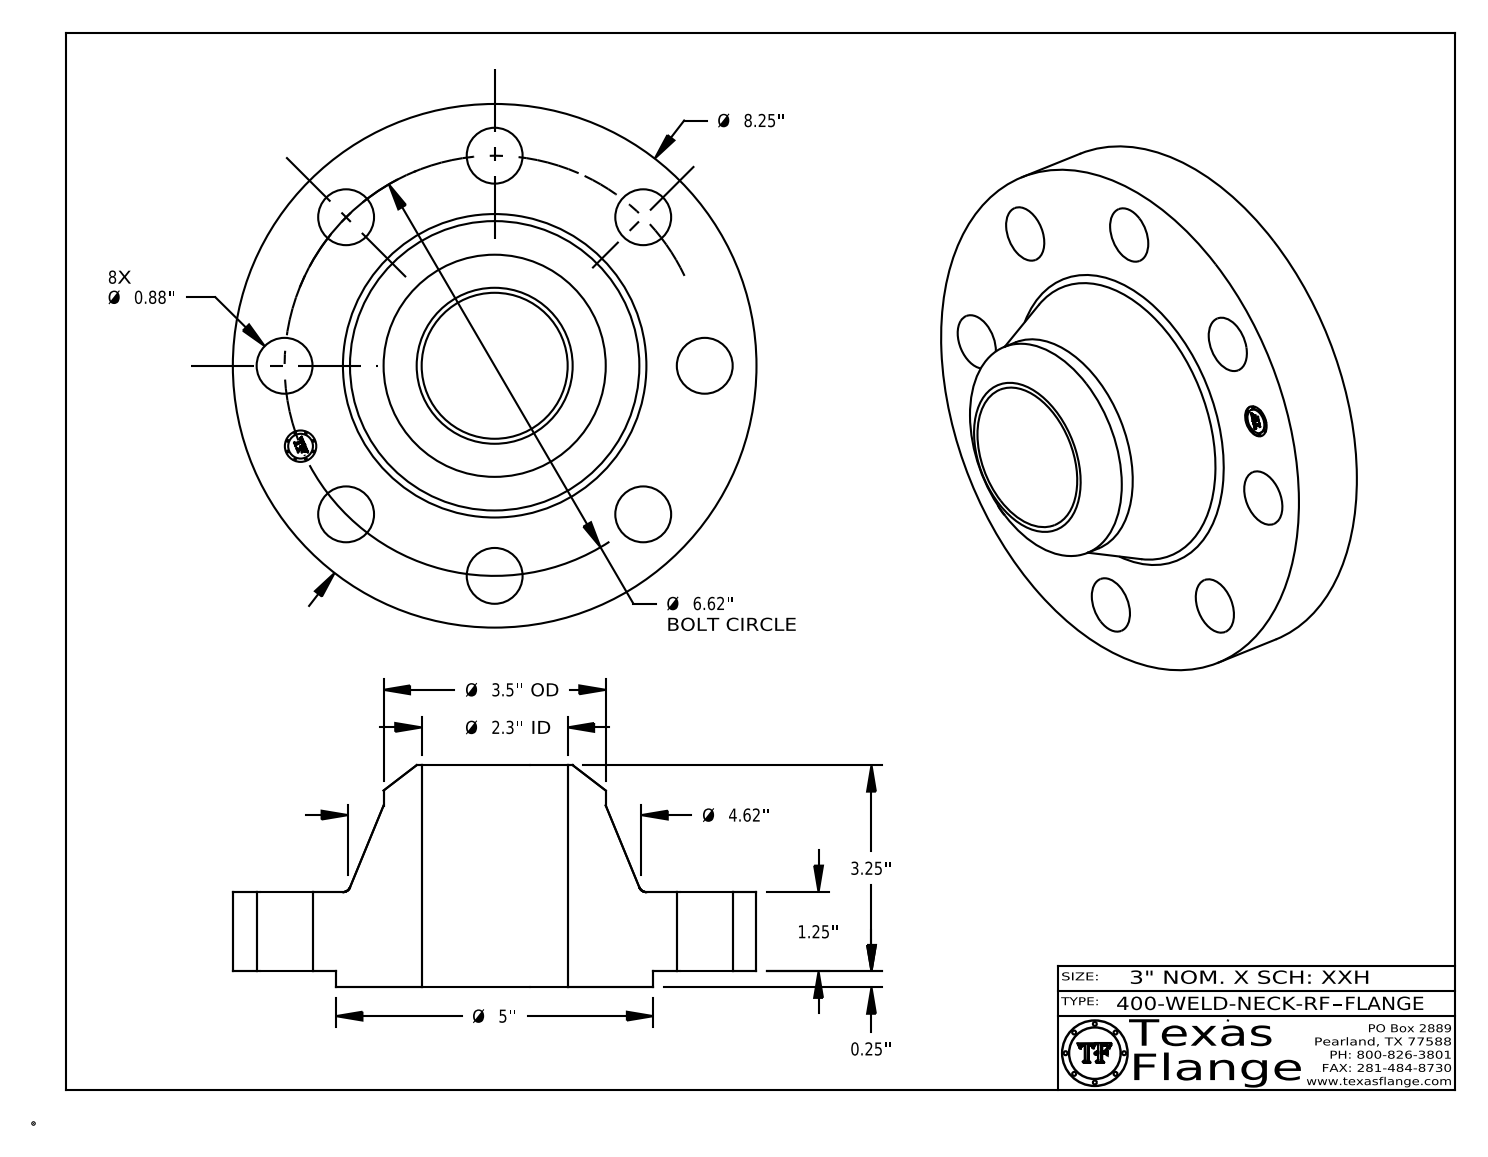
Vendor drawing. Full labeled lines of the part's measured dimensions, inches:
Part name (STEP PRODUCT): 400-WELD-NECK-RF
STEP written by: CATIA V5 STEP AP214 (AUTOMOTIVE_DESIGN)
Units: inches
Bodies: 1 solid, 419 faces (369 planar, 44 cylindrical, 6 other)
Overall size (bounding box): 8.25 × 8.25 × 3.5
Volume: 73.98 in³ · Surface area: 193.5 in²
Round holes (diameter × count): ⌀0.88 ×8, ⌀0.495 ×1, ⌀2.3 ×1
Round bosses / shafts (diameter × count): ⌀0.03 ×8, ⌀8.25 ×1, ⌀5 ×1, ⌀3.5 ×1, ⌀0.39 ×1
Main face-to-face distances: 1.25, 0.25, 1.5, 3.5, 3.25, 2, 0.015, 1.485, 1.235, 2.015
Hole centre spacings: 3.31, 2.533, 6.116, 4.681, 4.681, 1.291, 3.678, 6.493
